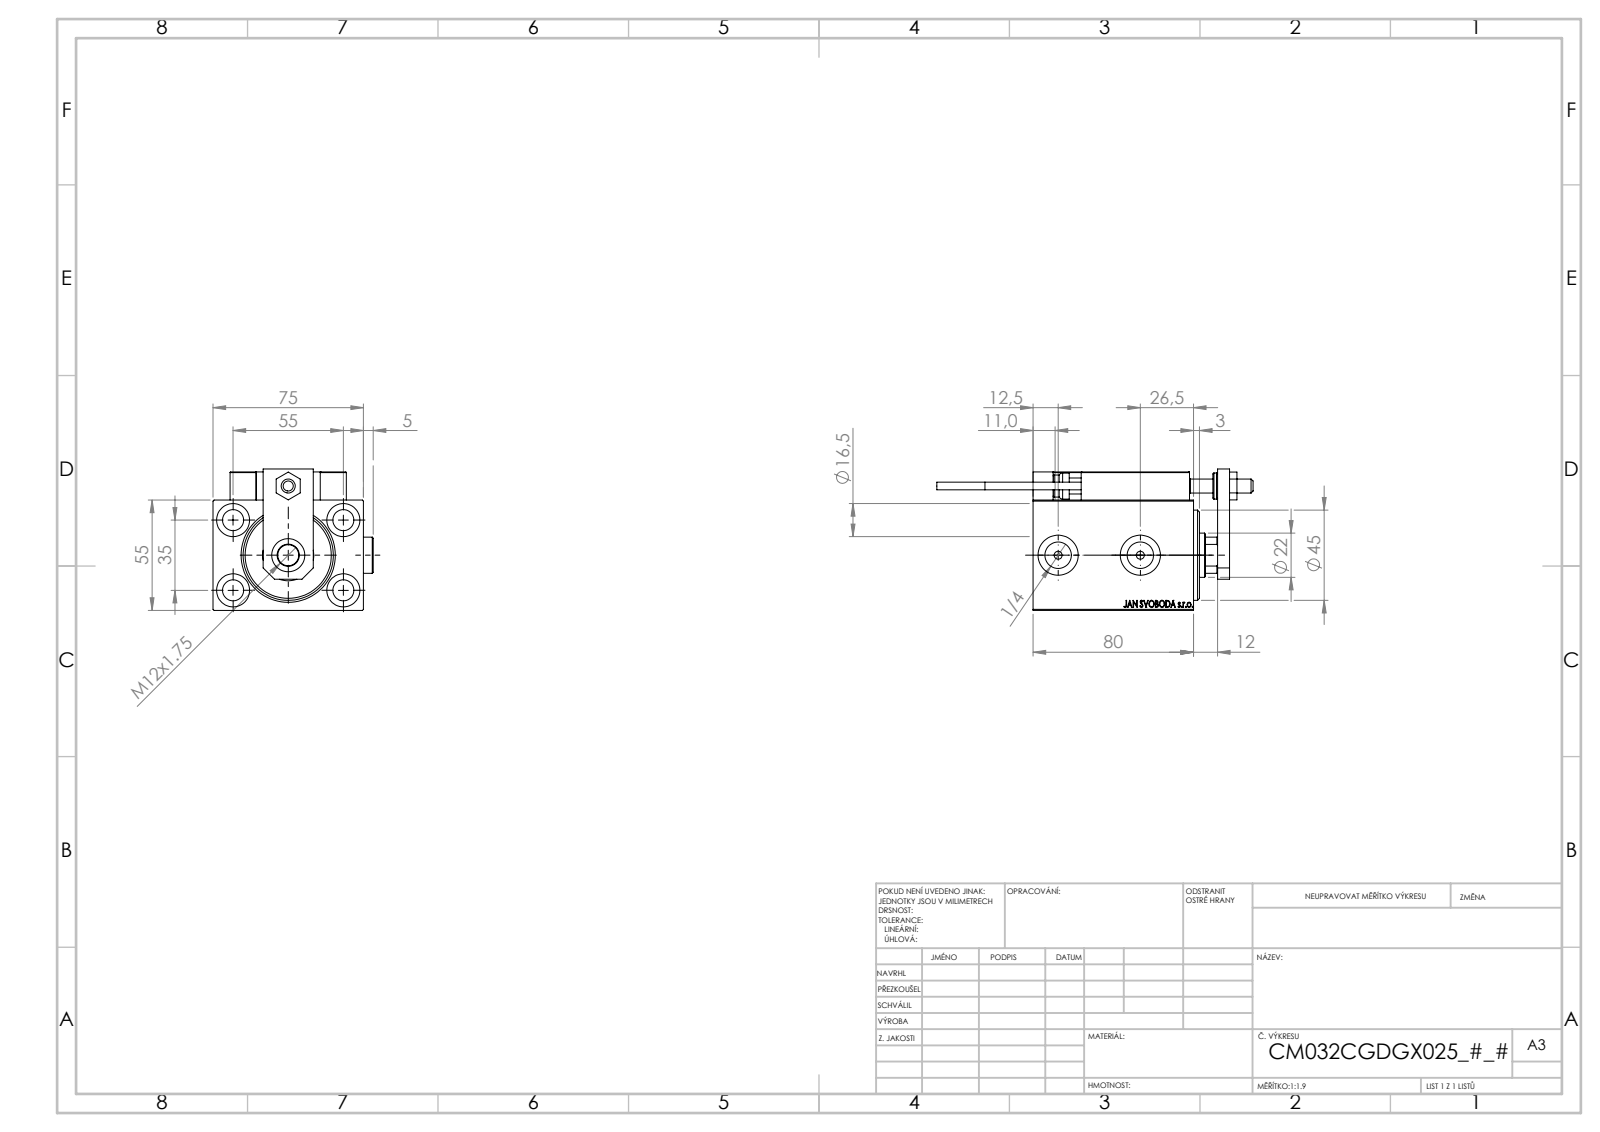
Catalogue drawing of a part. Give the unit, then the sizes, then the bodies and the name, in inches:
Units: inches
Overall size (bounding box): 6.209 × 3.146 × 2.776
Round holes (diameter × count): ⌀0.157 ×6, ⌀0.315 ×5, ⌀0.413 ×5, ⌀0.65 ×5, ⌀0.126 ×4, ⌀0.197 ×2, ⌀0.518 ×2, ⌀0.787 ×2, ⌀0.276 ×1, ⌀0.866 ×1, ⌀1.004 ×1, ⌀1.26 ×1
Round bosses / shafts (diameter × count): ⌀0.709 ×2, ⌀0.197 ×2, ⌀0.15 ×2, ⌀0.512 ×1, ⌀0.433 ×1
Partial cylindrical surfaces — rounded edges, fillets, slot ends (radius × count): R0.012 ×30, R0.118 ×2, R0.413 ×1
Main face-to-face distances: 2.165, 2.953, 0.551, 0.394, 2.717, 0.472, 0.984, 2.283, 0.197, 0.276
Hole centre spacings: 1.283, 0.448, 0.787, 1.165, 1.169, 1.262, 1.273, 1.378
Volume: 20.06 in³ · Surface area: 140 in²
Bodies: 25 solids, 1336 faces (594 planar, 204 cylindrical, 538 other)
Part name (STEP PRODUCT): ALLEN BOLT D8; MAGNET; SWITCH_X_FRONT_BACK; V450CM_C_Body (+7 more)
STEP written by: SolidWorks 2019 (CONFIG_CONTROL_DESIGN)
